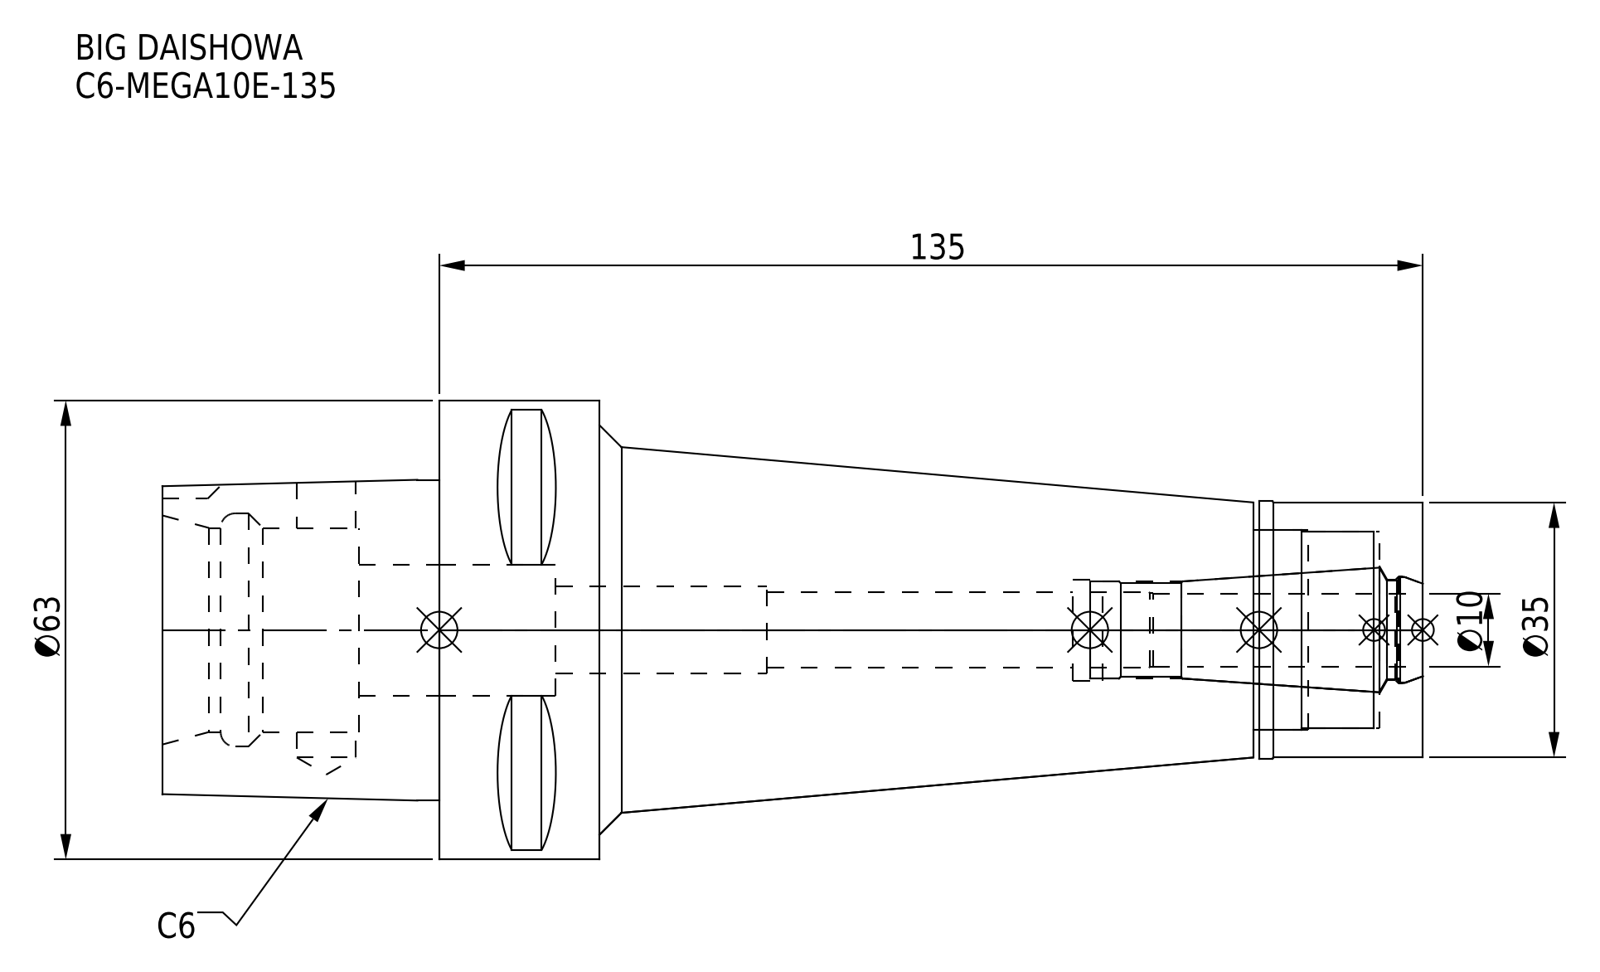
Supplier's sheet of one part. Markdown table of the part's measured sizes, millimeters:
| quantity | value |
| --- | --- |
| part name | C6-MEGA10E-135-100-FreeParts; C6-MEGA10E-135; C6-MEGA10E-135_1.stp; C6-MEGA10E-135-100.stp (+3 more) |
| STEP written by | SolidWorks 2019 (CONFIG_CONTROL_DESIGN) |
| units | millimeters |
| bodies | 2 solids, 100 faces (37 planar, 39 cylindrical, 24 other) |
| overall size | 173 × 63 × 63 |
| volume | 235 070 mm³ |
| surface area | 42 321 mm² |
| round holes (diameter × count) | 8.1 × 1, 10.4 × 1, 12 × 1, 13.3 × 1, 13.8 × 1, 13.9 × 1, 14.7 × 1, 18 × 1, 27 × 1, 27.5 × 1, 28 × 1, 32 × 1 |
| round bosses / shafts (diameter × count) | 63 × 1, 35.3 × 1, 35 × 1 |
| partial cylindrical surfaces (radius × count) | 5 × 1 |
| main face-to-face distances | 135, 113, 22, 38, 27, 173, 60, 6, 22.5, 90.5 |
